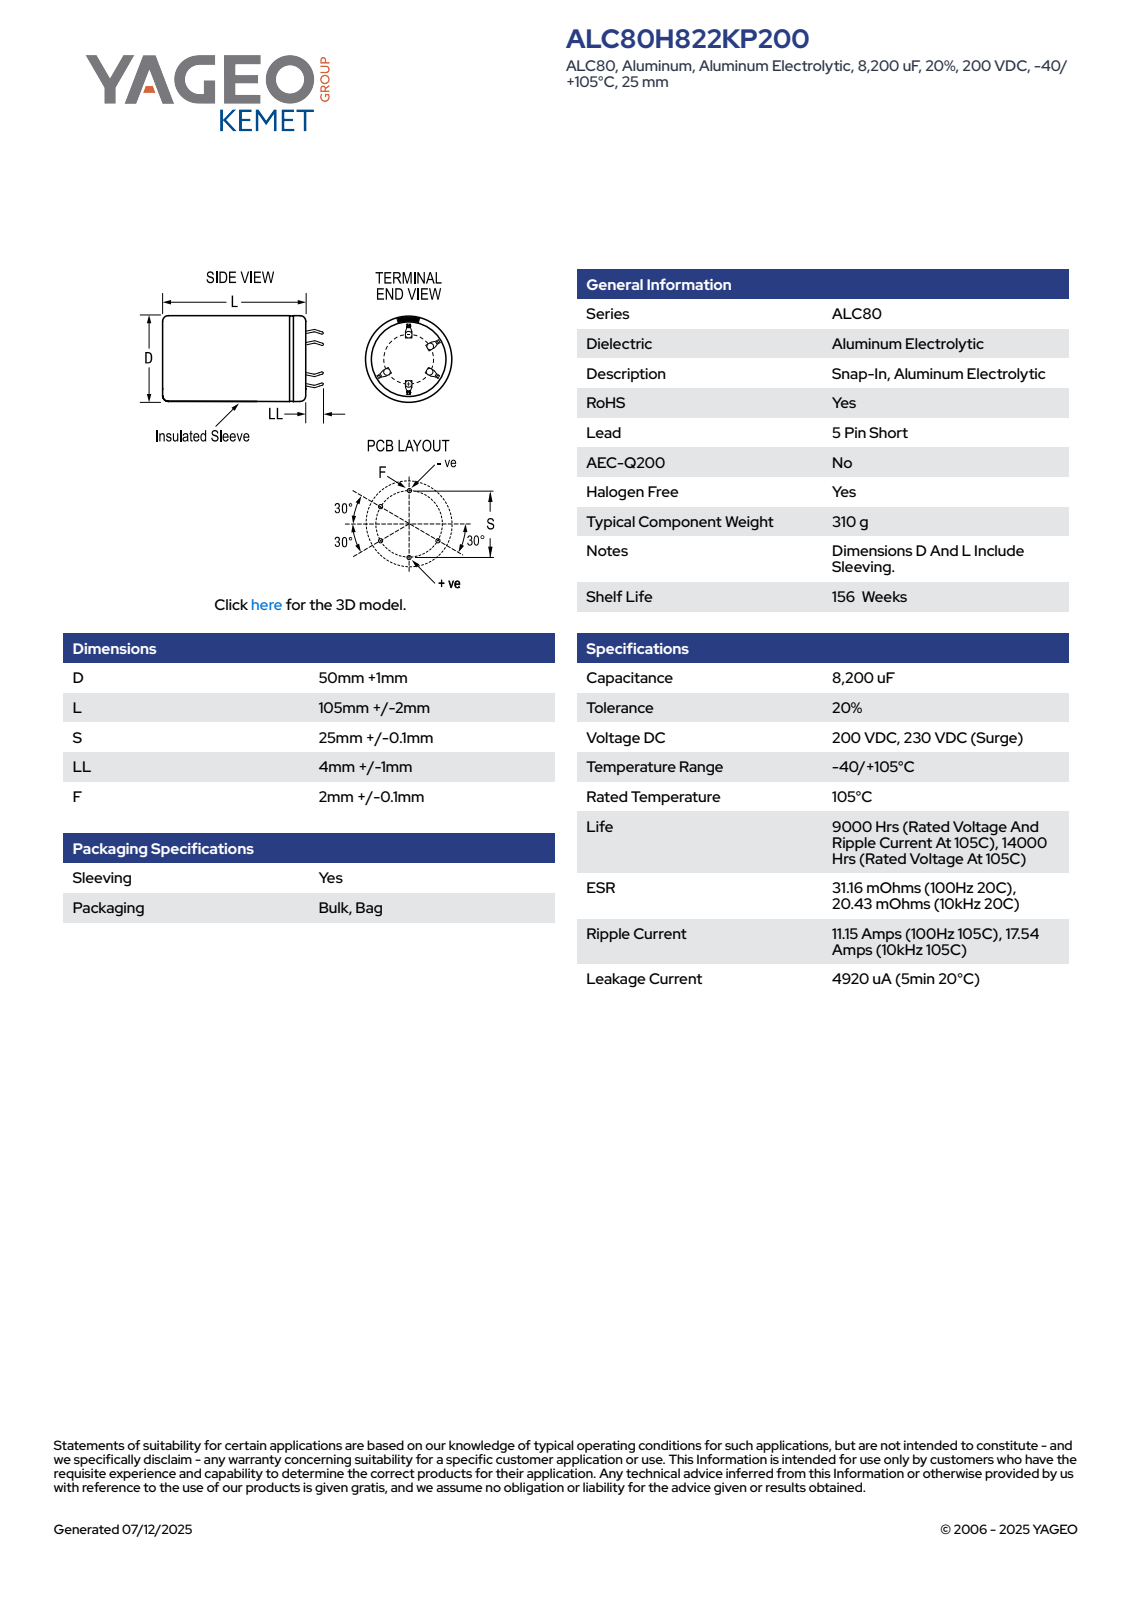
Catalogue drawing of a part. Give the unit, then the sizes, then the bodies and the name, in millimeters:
Units: millimetres
Overall size (bounding box): 111.99 × 51 × 51
Round holes (diameter × count): ⌀45.12 ×1
Round bosses / shafts (diameter × count): ⌀51 ×1
Partial cylindrical surfaces — rounded edges, fillets, slot ends (radius × count): R25.49 ×1
Main face-to-face distances: 106.99, 107.49, 0.5, 0.46, 0.6, 0.75, 1.35, 22.04, 22.03, 2.1
Volume: 217 079 mm³ · Surface area: 21 225 mm²
Bodies: 1 solid, 148 faces (94 planar, 15 cylindrical, 39 other)
Part name (STEP PRODUCT): CARS_K5P_50X105_D51L107S25LL5F2.1
STEP written by: SolidWorks 2014 (AUTOMOTIVE_DESIGN)
